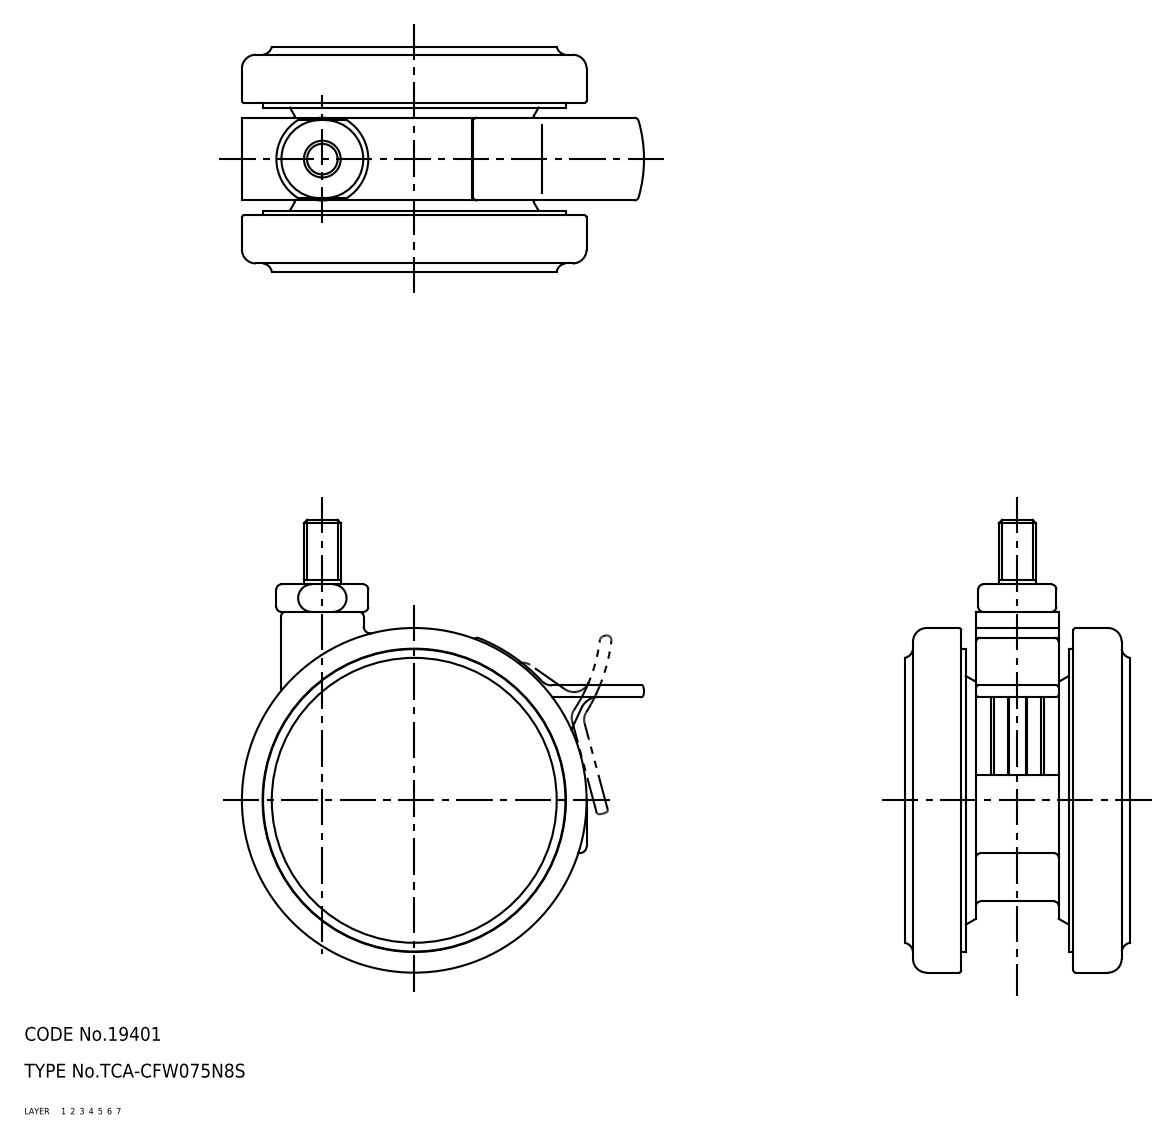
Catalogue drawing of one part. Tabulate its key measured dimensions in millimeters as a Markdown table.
| quantity | value |
| --- | --- |
| part name | caster; TCA-CFW075N8S |
| STEP written by | SolidWorks 2015 (AUTOMOTIVE_DESIGN) |
| units | millimeters |
| bodies | 1 solid, 1455 faces (446 planar, 693 cylindrical, 316 other) |
| overall size | 98.5 × 87.5 × 49 |
| volume | 128 503 mm³ |
| surface area | 81 345 mm² |
| round holes (diameter × count) | 1.8 × 1, 3 × 1, 3.3 × 1, 8.1 × 1, 8.4 × 1, 9 × 1, 9.3 × 1, 10.7 × 1, 12.3 × 1, 18 × 1, 58.41 × 1, 59 × 1 |
| round bosses / shafts (diameter × count) | 8 × 3, 75 × 1, 68 × 1, 65.8 × 1, 62.9 × 1, 58.2 × 1, 51 × 1, 18 × 1 |
| partial cylindrical surfaces (radius × count) | 1 × 71, 0.8 × 70, 0.5 × 54, 0.1 × 24, 0.2 × 16, 1.5 × 9, 0.3 × 6, 3 × 4 |
| main face-to-face distances | 1.5, 4.5, 12.3, 35.2, 47.5, 3.3, 45.7, 1.8, 44.2, 33.4 |
| hole center spacings | 32.49 |
